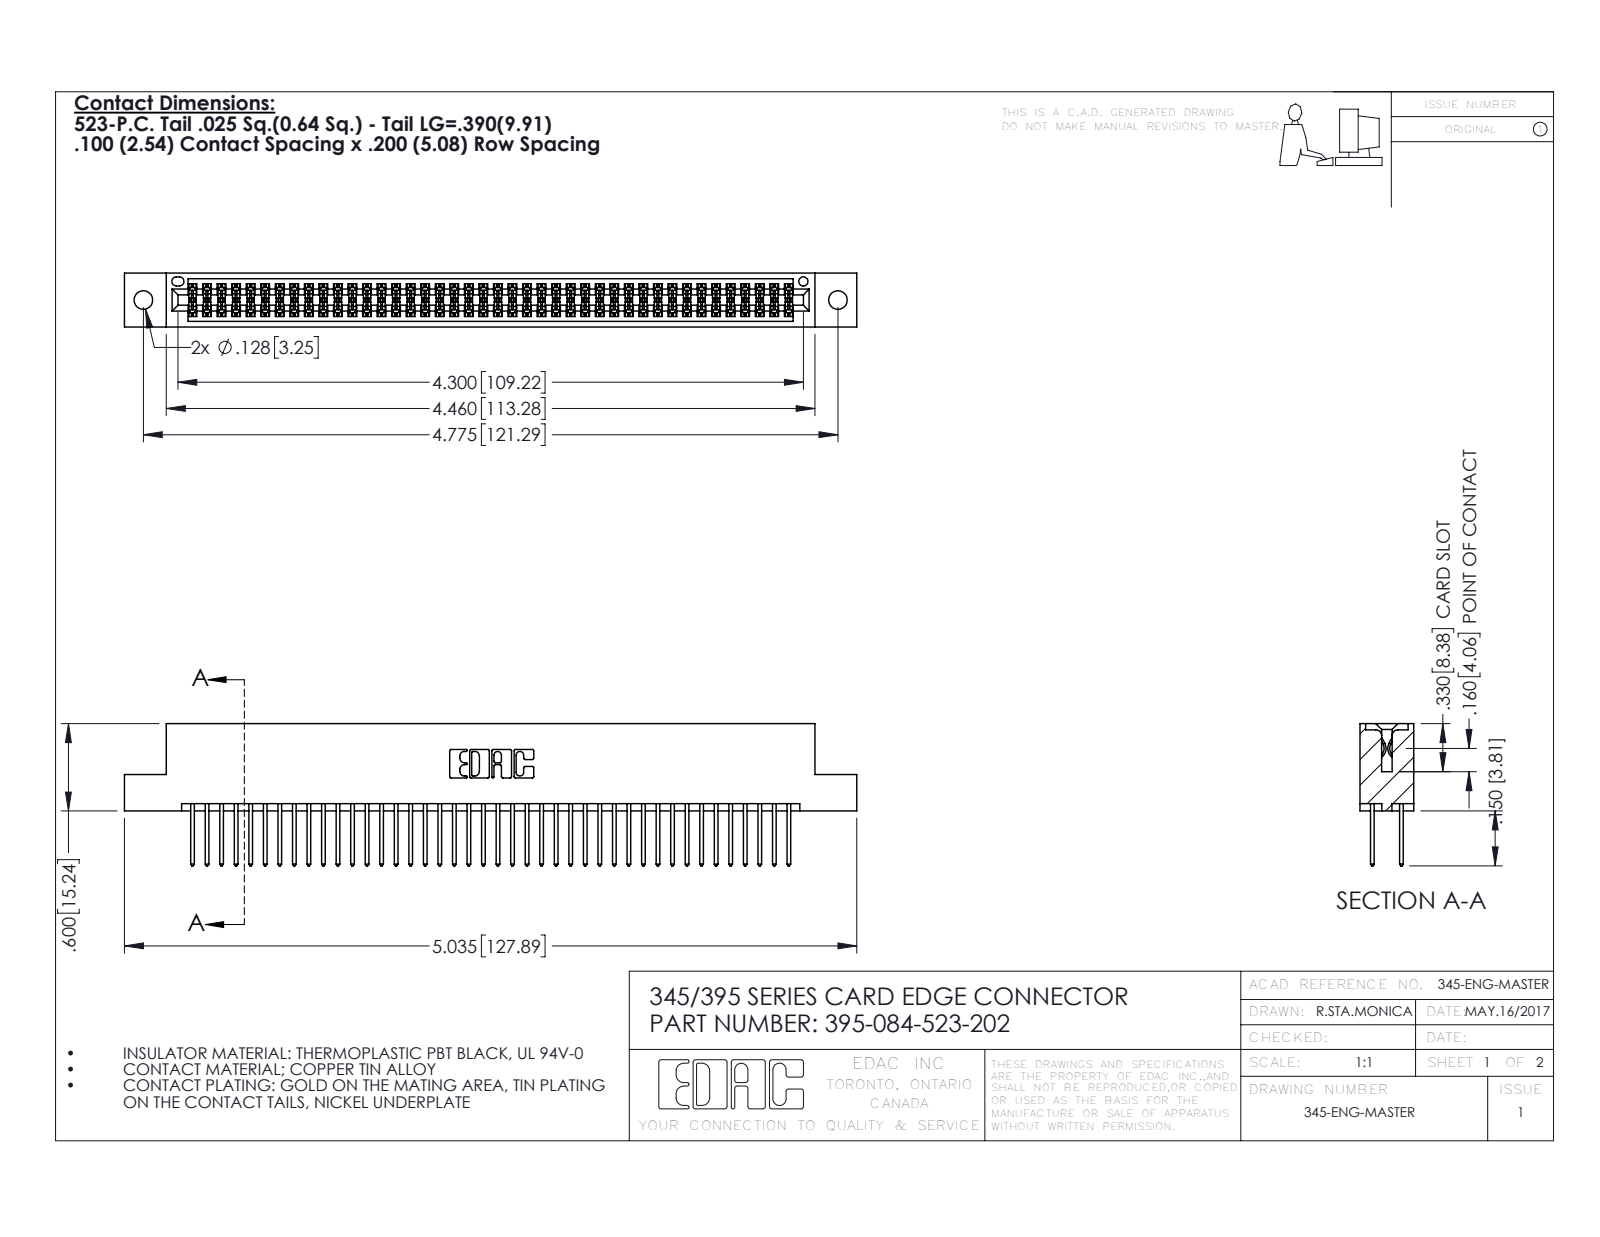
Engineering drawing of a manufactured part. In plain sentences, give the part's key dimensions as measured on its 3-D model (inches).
The part is named "395-084-523-202; 345-292-001_345-293-123; 345 Part_Flush Mounting Lugs - 0.128 Dia". Its 3-D file was written by "SolidWorks 2016 (CONFIG_CONTROL_DESIGN)". It is 85 solids with 4326 faces: 2852 planar, 1474 cylindrical and 0 other. Overall it measures 5.035 by 0.977 by 0.37 inches. Its volume is 0.766 cubic inches and its surface area 29.55 square inches. Round holes: 2 of diameter 0.128, 1 of diameter 0.064. Partial cylindrical surfaces (rounded edges, fillets, slot ends): 126 of radius 0.006, 84 of radius 0.01, 22 of radius 0.01, 6 of radius 0.007, 6 of radius 0.031, 3 of radius 0.026, 2 of radius 0.014, 2 of radius 0.019. The main face-to-face distances are 0.298, 0.072, 0.2, 0.098, 0.272, 0.025, 0.37, 0.225, 0.175, 0.149. The hole center spacings are 0.27, 4.539, 4.775.
